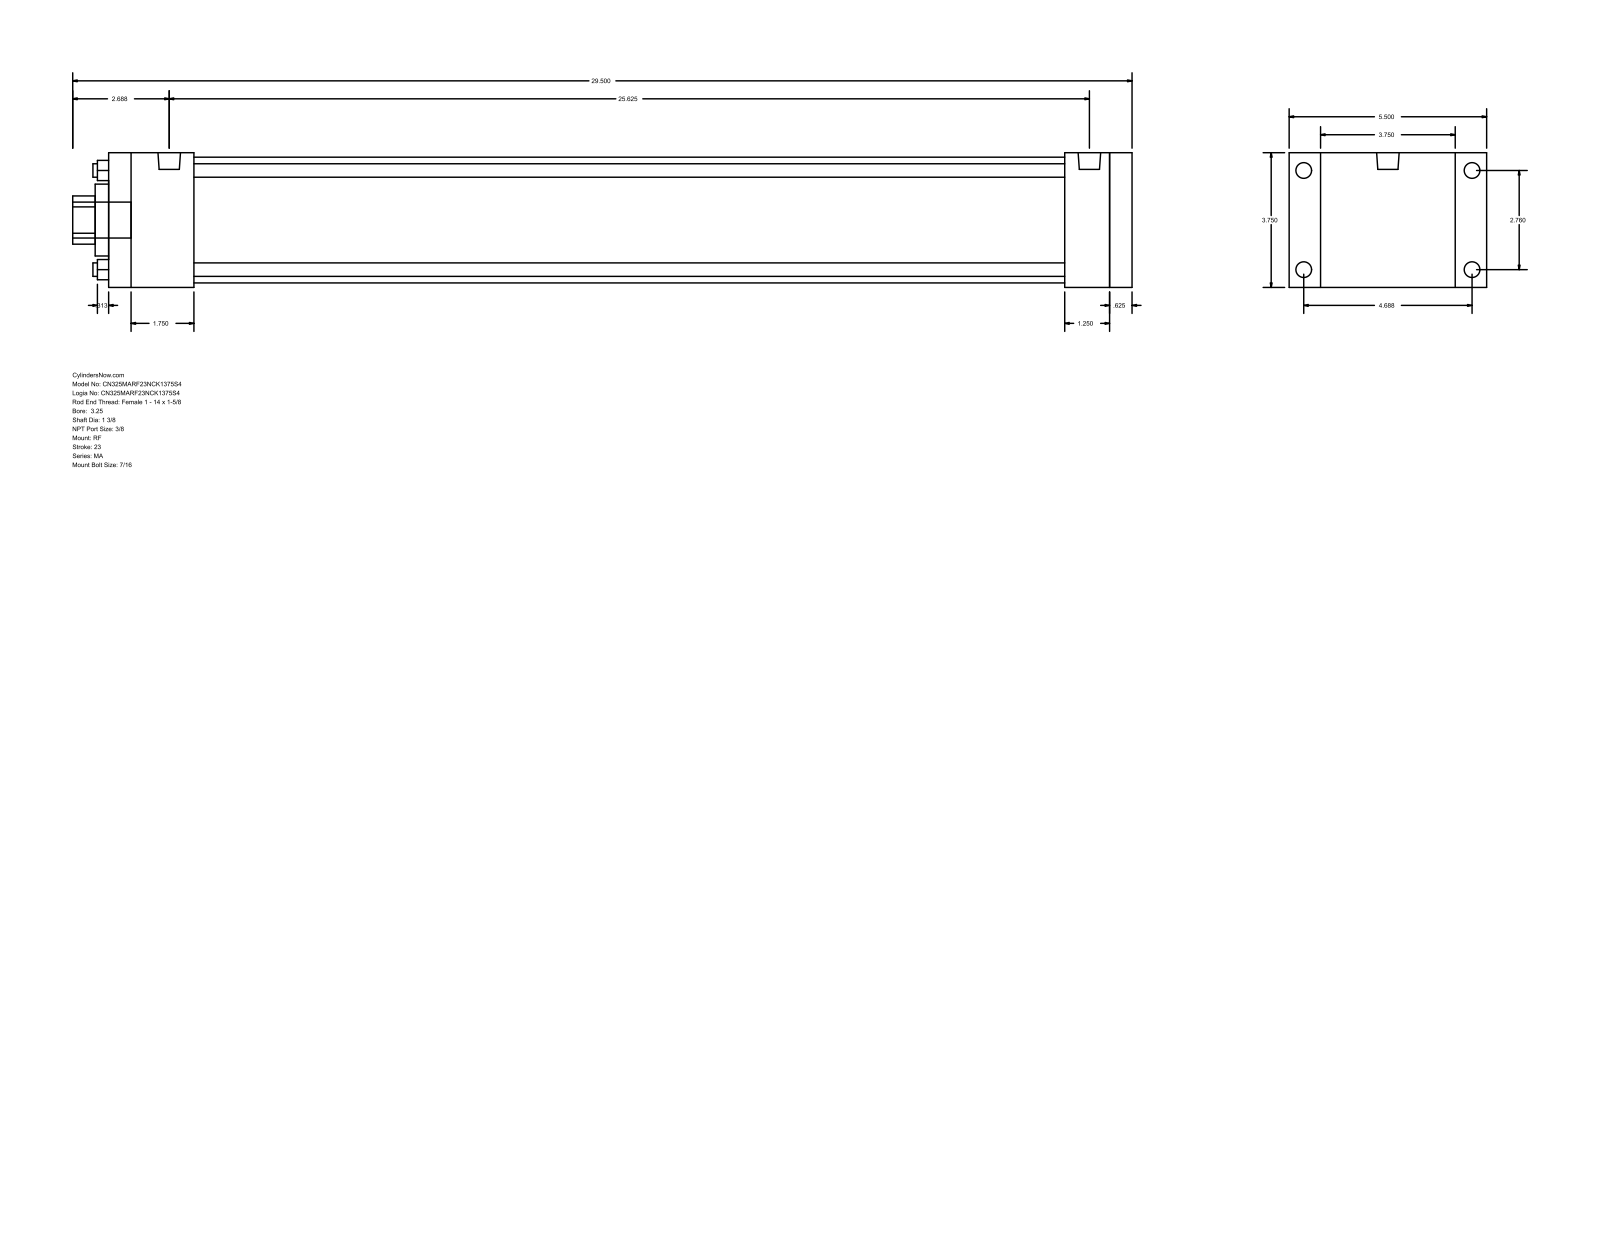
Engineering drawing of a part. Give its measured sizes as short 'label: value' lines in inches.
name: MA_RF__0325_1.375
written by: GSSL Pune (CONFIG_CONTROL_DESIGN)
unit: in
bodies: 0 solids, 92 faces (64 planar, 28 cylindrical, 0 other)
size: 29.5 × 5.5 × 3.75
holes: 4× ⌀0.375, 1× ⌀1.375, 1× ⌀2, 1× ⌀3.5
bosses: 8× ⌀0.437, 2× ⌀0.627, 1× ⌀1
rounds: 1× R0.672
face distances: 3.75, 28.5, 0.625, 27.875, 0.875, 4.625, 26.625, 1.25, 1.875, 2.375
hole spacings: 1.952, 2.76, 3.903
